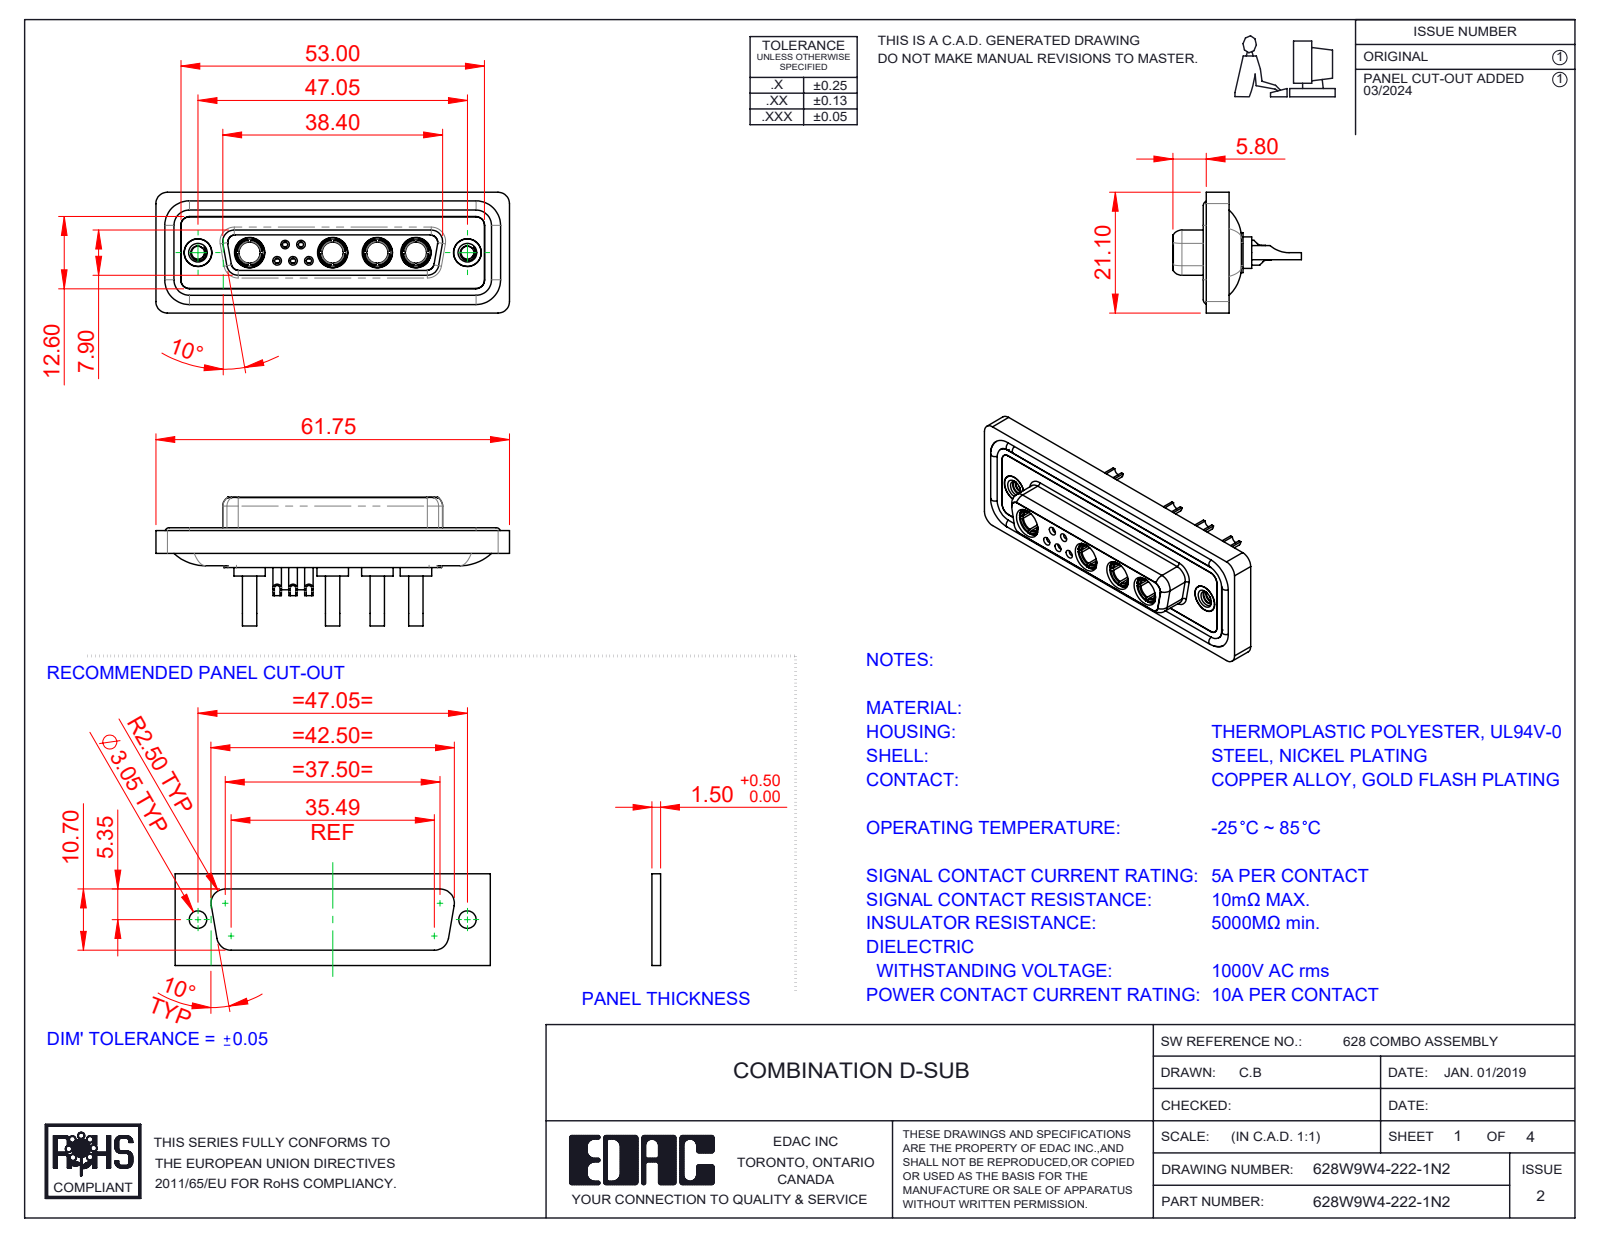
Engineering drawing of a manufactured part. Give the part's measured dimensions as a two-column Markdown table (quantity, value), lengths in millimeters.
| quantity | value |
| --- | --- |
| part name | 628Combo Threaded Rivet_2; 628Combo Shell Rear_25 Contacts; 628Combo Contact Row 2_22; 628Combo Contact Row 1_22 (+5 more) |
| STEP written by | SolidWorks 2023 (CONFIG_CONTROL_DESIGN) |
| units | millimeters |
| bodies | 20 solids, 977 faces (314 planar, 397 cylindrical, 266 other) |
| overall size | 61.75 × 22.45 × 21.1 |
| volume | 8 223 mm³ |
| surface area | 13 808 mm² |
| round holes (diameter × count) | 4.85 × 6, 0.9 × 5, 1 × 5, 1.1 × 5, 1.5 × 5, 2 × 5, 1.7 × 4, 3.7 × 4, 5.3 × 4, 1.6 × 3, 1.7 × 2, 2.26 × 2 |
| round bosses / shafts (diameter × count) | 1.6 × 6, 2.2 × 5, 5.5 × 4, 5.2 × 4, 4.96 × 4, 4.75 × 4, 3.75 × 4, 2.5 × 4 |
| partial cylindrical surfaces (radius × count) | 1.5 × 22, 2 × 18, 1.35 × 8, 1.6 × 8, 1 × 6, 0.25 × 4, 0.5 × 4, 0.6 × 4 |
| main face-to-face distances | 0.4, 1.8, 7.45, 5.65, 0.5, 7.05, 6.6, 1.6, 1.1, 2.9 |
| hole center spacings | 3.16, 2.77, 5.03, 2.76, 4.4, 5.02, 5.54, 5.73 |
